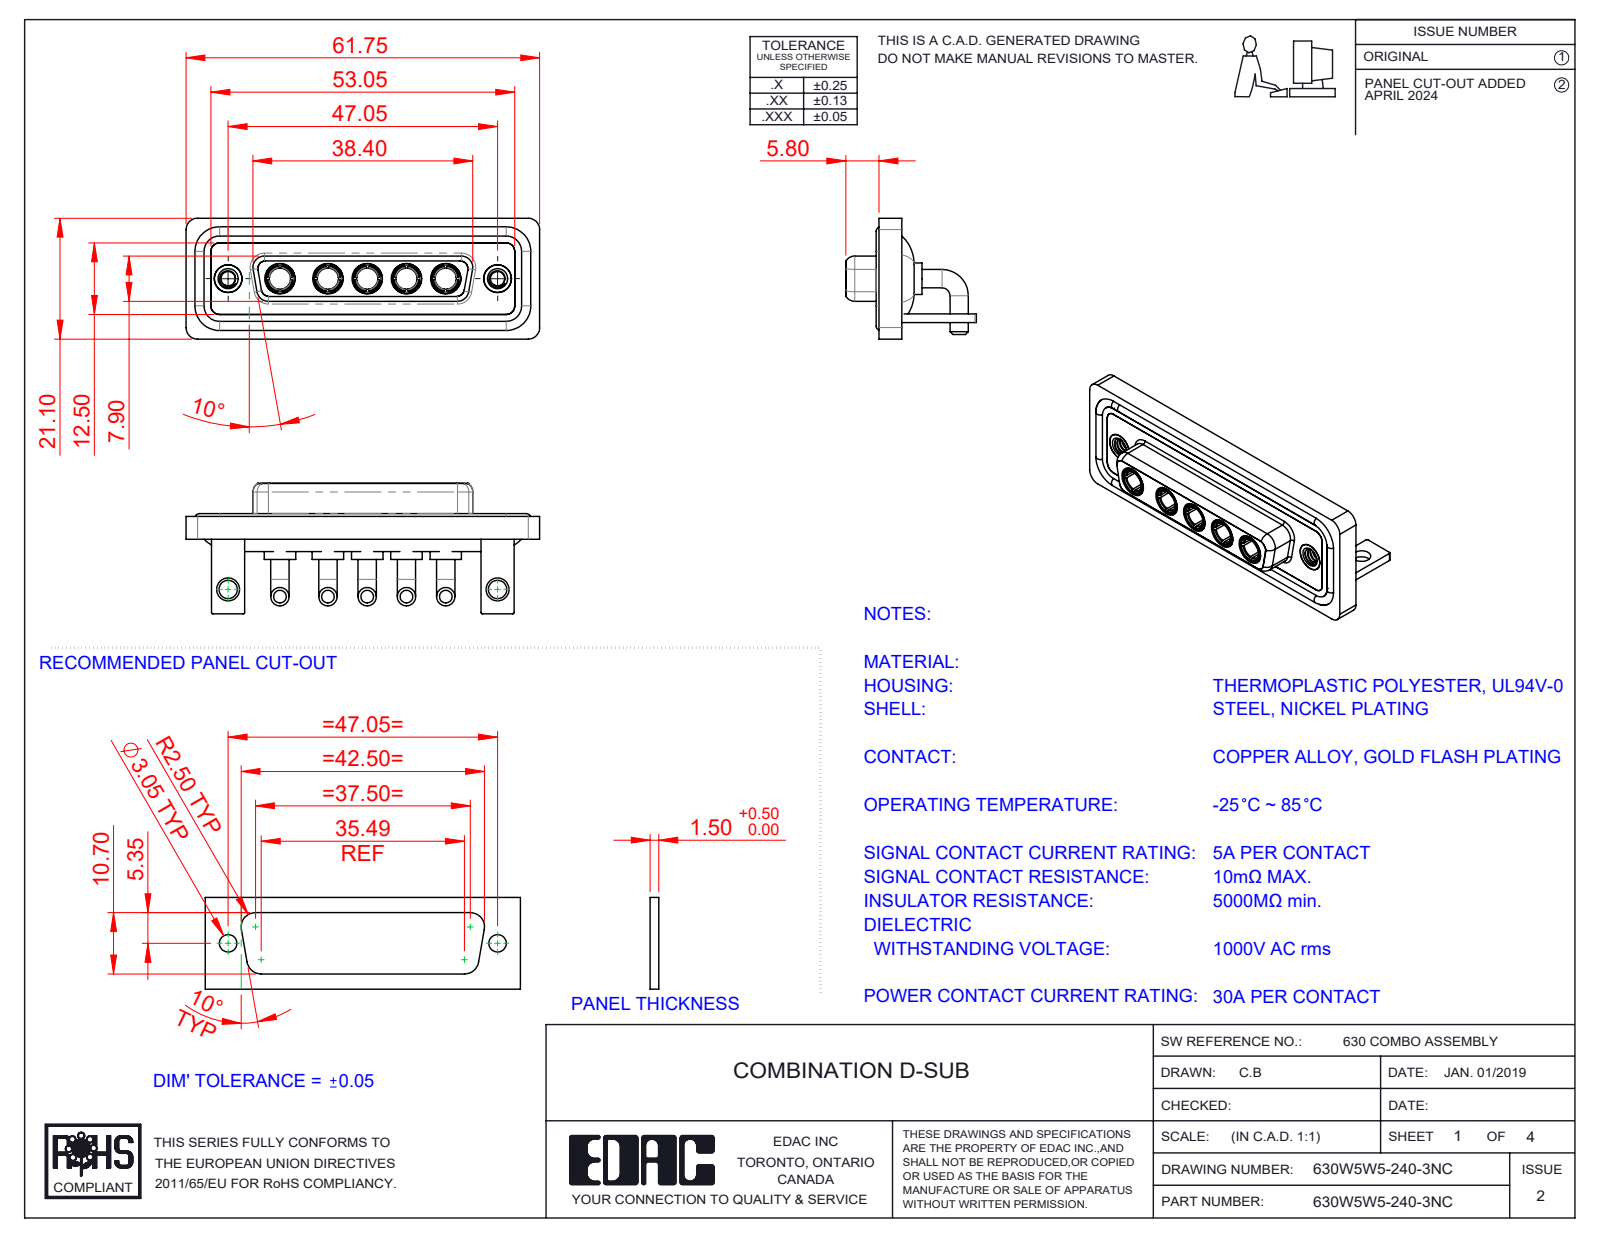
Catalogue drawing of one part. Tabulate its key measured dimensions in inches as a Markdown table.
| quantity | value |
| --- | --- |
| part name | 630Combo Stabilizer Bracket_50 Contacts; 630W5W5-140-3NC; 630Combo Shell Front_25 Contacts; 630Combo Waterproof Housing_25 Contacts (+4 more) |
| STEP written by | SolidWorks 2023 (CONFIG_CONTROL_DESIGN) |
| units | inches |
| bodies | 19 solids, 818 faces (270 planar, 335 cylindrical, 213 other) |
| overall size | 2.431 × 0.898 × 0.831 |
| volume | 0.545 in³ |
| surface area | 22.7 in² |
| round holes (diameter × count) | 0.191 × 7, 0.146 × 5, 0.209 × 5, 0.098 × 2, 0.126 × 2, 0.157 × 2, 0.159 × 2, 0.197 × 2 |
| round bosses / shafts (diameter × count) | 0.126 × 10, 0.217 × 5, 0.205 × 5, 0.195 × 5, 0.187 × 5, 0.148 × 5, 0.063 × 4, 0.195 × 2 |
| partial cylindrical surfaces (radius × count) | 0.079 × 19, 0.059 × 18, 0.01 × 16, 0.053 × 8, 0.063 × 8, 0.02 × 5, 0.083 × 5, 0.024 × 4 |
| main face-to-face distances | 0.016, 0.071, 0.114, 0.146, 0.059, 0.161, 0.043, 0.055, 0.063, 0.098 |
| hole center spacings | 0.27, 0.356, 1.496, 1.852, 0.27, 0.33, 0.54, 0.541 |
